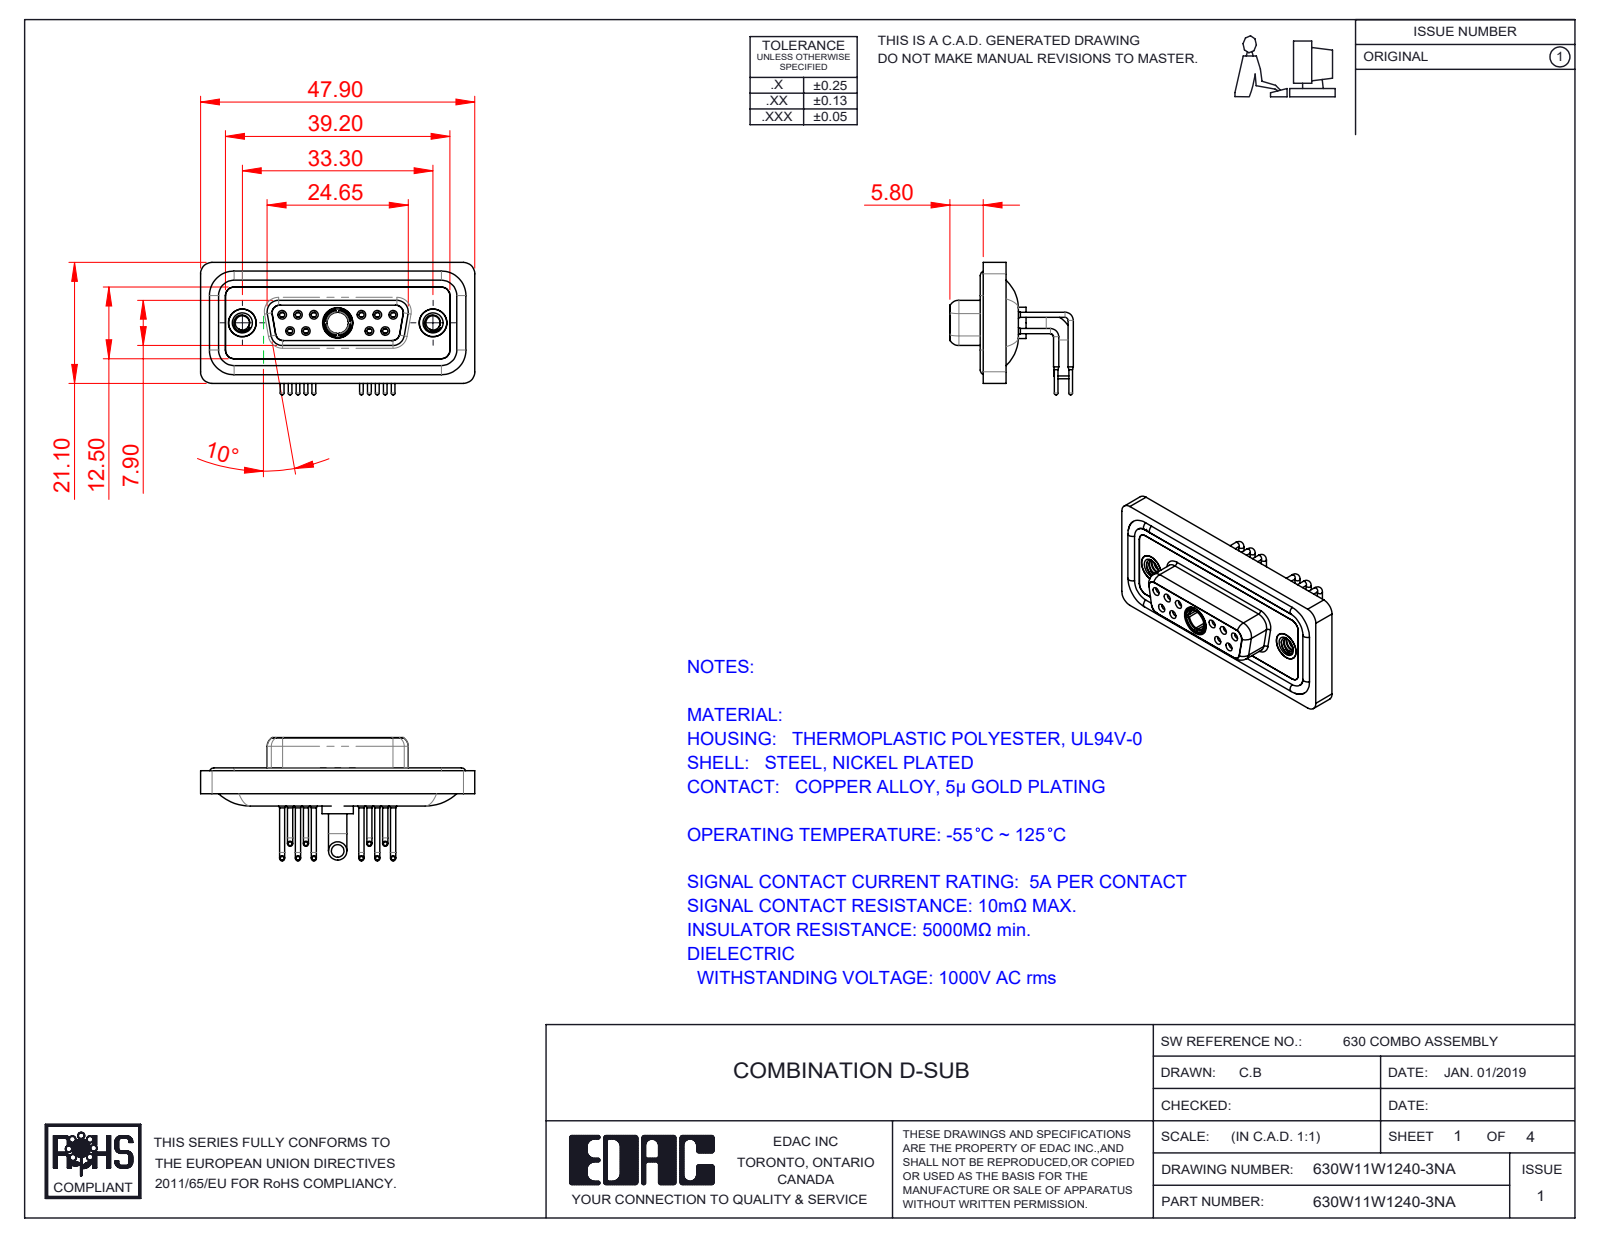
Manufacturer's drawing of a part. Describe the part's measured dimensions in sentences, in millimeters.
The part is named "630Combo Threaded Rivet_A; 630Combo Housing_11W1; 630W11W1240-3NA; 630Combo Waterproof Housing_15 Contacts (+5 more)". Its 3-D file was written by "SolidWorks 2020 (CONFIG_CONTROL_DESIGN)". It is 19 solids with 988 faces: 284 planar, 441 cylindrical and 263 other. Overall it measures 47.9 by 23.12 by 21.53 millimeters. Its volume is 6 238 cubic millimeters and its surface area 10 492 square millimeters. Round holes: 10 of diameter 0.9, 10 of diameter 1.1, 10 of diameter 1.5, 10 of diameter 2, 6 of diameter 1.7, 4 of diameter 1.6, 3 of diameter 4.85, 2 of diameter 2.5, 2 of diameter 4, 2 of diameter 4.05, 2 of diameter 5, 1 of diameter 3.7. Round bosses or shafts: 10 of diameter 1.6, 10 of diameter 0.9, 10 of diameter 0.65, 2 of diameter 4.95, 2 of diameter 4.8, 2 of diameter 3.2, 1 of diameter 5.5, 1 of diameter 5.2. Partial cylindrical surfaces (rounded edges, fillets, slot ends): 20 of radius 2, 18 of radius 1.5, 12 of radius 1.35, 8 of radius 1.6, 4 of radius 0.25, 4 of radius 0.5, 4 of radius 0.6, 4 of radius 0.65. The main face-to-face distances are 0.4, 1.8, 1.1, 1.6, 2.5, 2.9, 3.1, 3.7, 4.1, 1.5. The hole center spacings are 3.16, 2.77, 13.85, 11.08, 16.62, 5.03, 5.04, 5.54.
